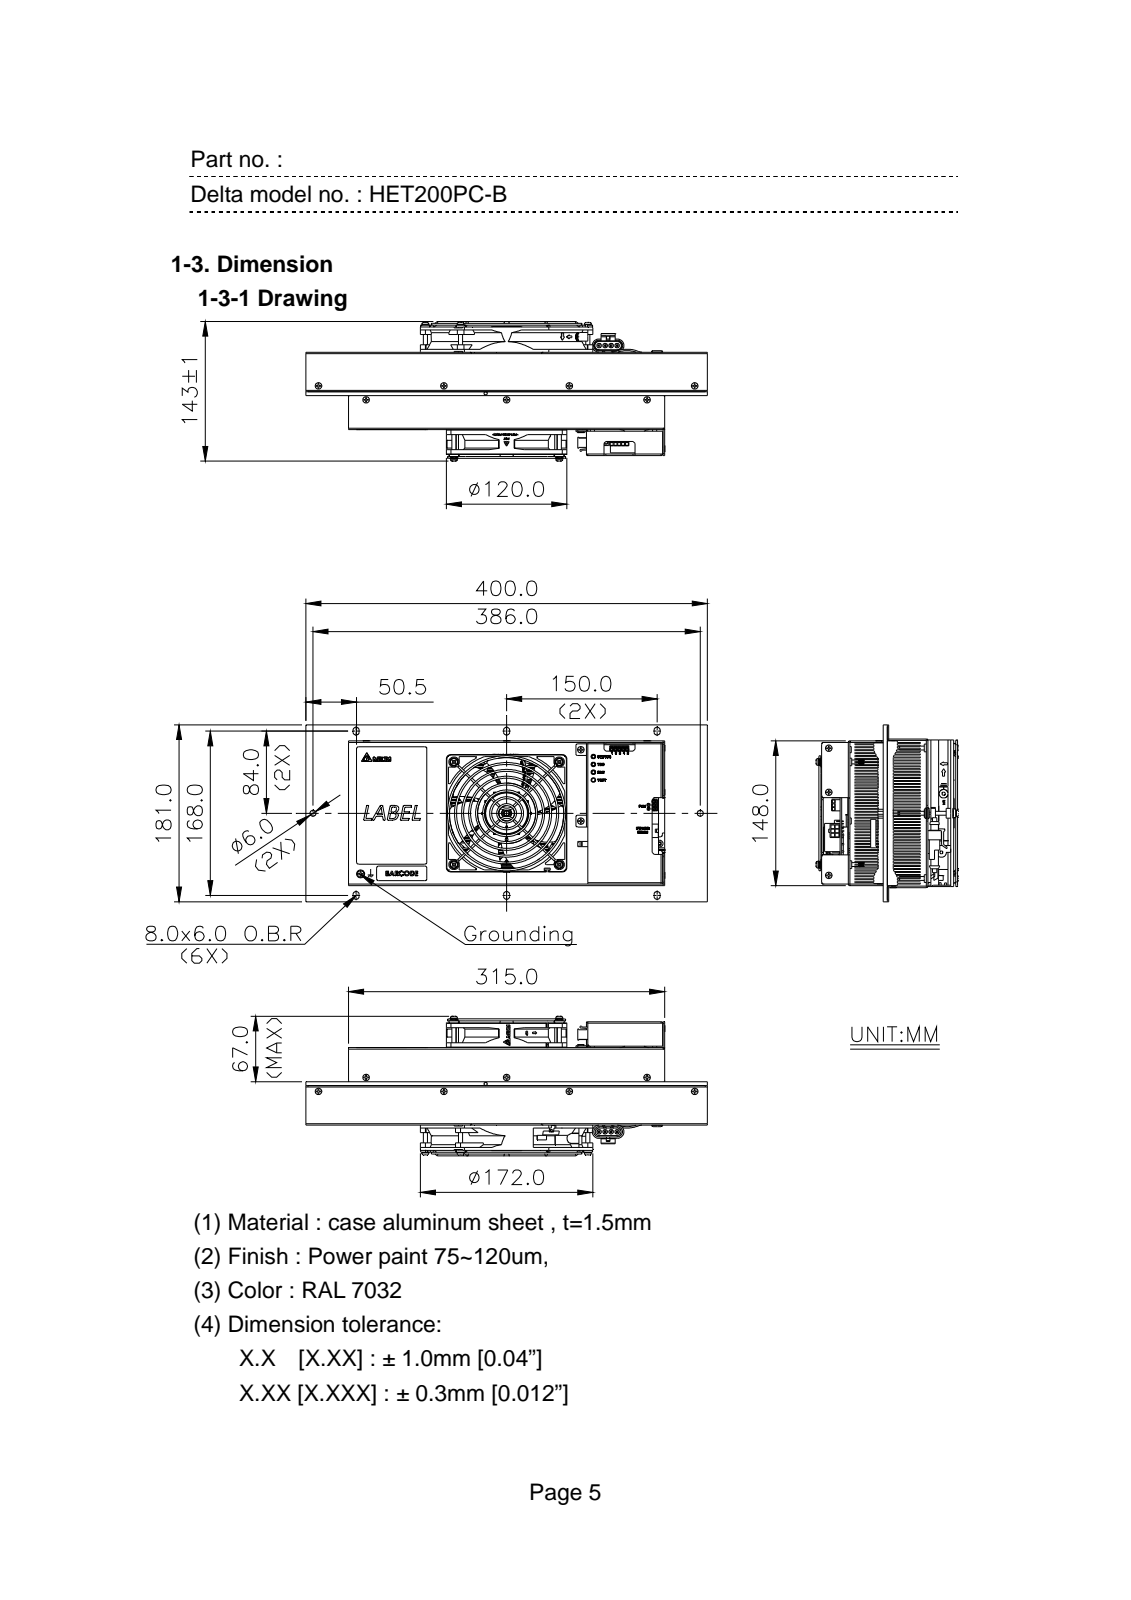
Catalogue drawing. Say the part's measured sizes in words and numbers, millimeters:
The part is named "G4_1; G7; X6; G4_2 (+6 more)". Its 3-D file was written by "PRO/ENGINEER BY PARAMETRIC TECHNOLOGY CORPORATION, 2012200 (CONFIG_CONTROL_DESIGN)". It is 58 solids with 3476 faces: 2163 planar, 802 cylindrical and 511 other. Overall it measures 400 by 181 by 143.23 millimeters. Its volume is 583 122 cubic millimeters and its surface area 649 334 square millimeters. Round holes: 9 of diameter 3, 9 of diameter 4, 9 of diameter 4.5, 5 of diameter 8, 4 of diameter 1.8, 4 of diameter 3.8, 4 of diameter 4.3, 4 of diameter 5.5, 4 of diameter 7, 3 of diameter 3.5, 1 of diameter 1.97, 1 of diameter 2.5. Round bosses or shafts: 20 of diameter 2.3, 9 of diameter 7.9, 9 of diameter 6.5, 9 of diameter 5.38, 7 of diameter 3, 5 of diameter 6.3, 5 of diameter 4.2, 4 of diameter 8. Partial cylindrical surfaces (rounded edges, fillets, slot ends): 39 of radius 2, 17 of radius 0.5, 16 of radius 1, 12 of radius 1.5, 12 of radius 3, 8 of radius 0.8, 6 of radius 4.5, 6 of radius 5.25. The main face-to-face distances are 1.5, 4, 78.5, 39.5, 2, 39, 44.5, 40.5, 148.5, 80. The hole center spacings are 59.74, 74.25, 81, 105, 143.45, 6, 8, 12.
